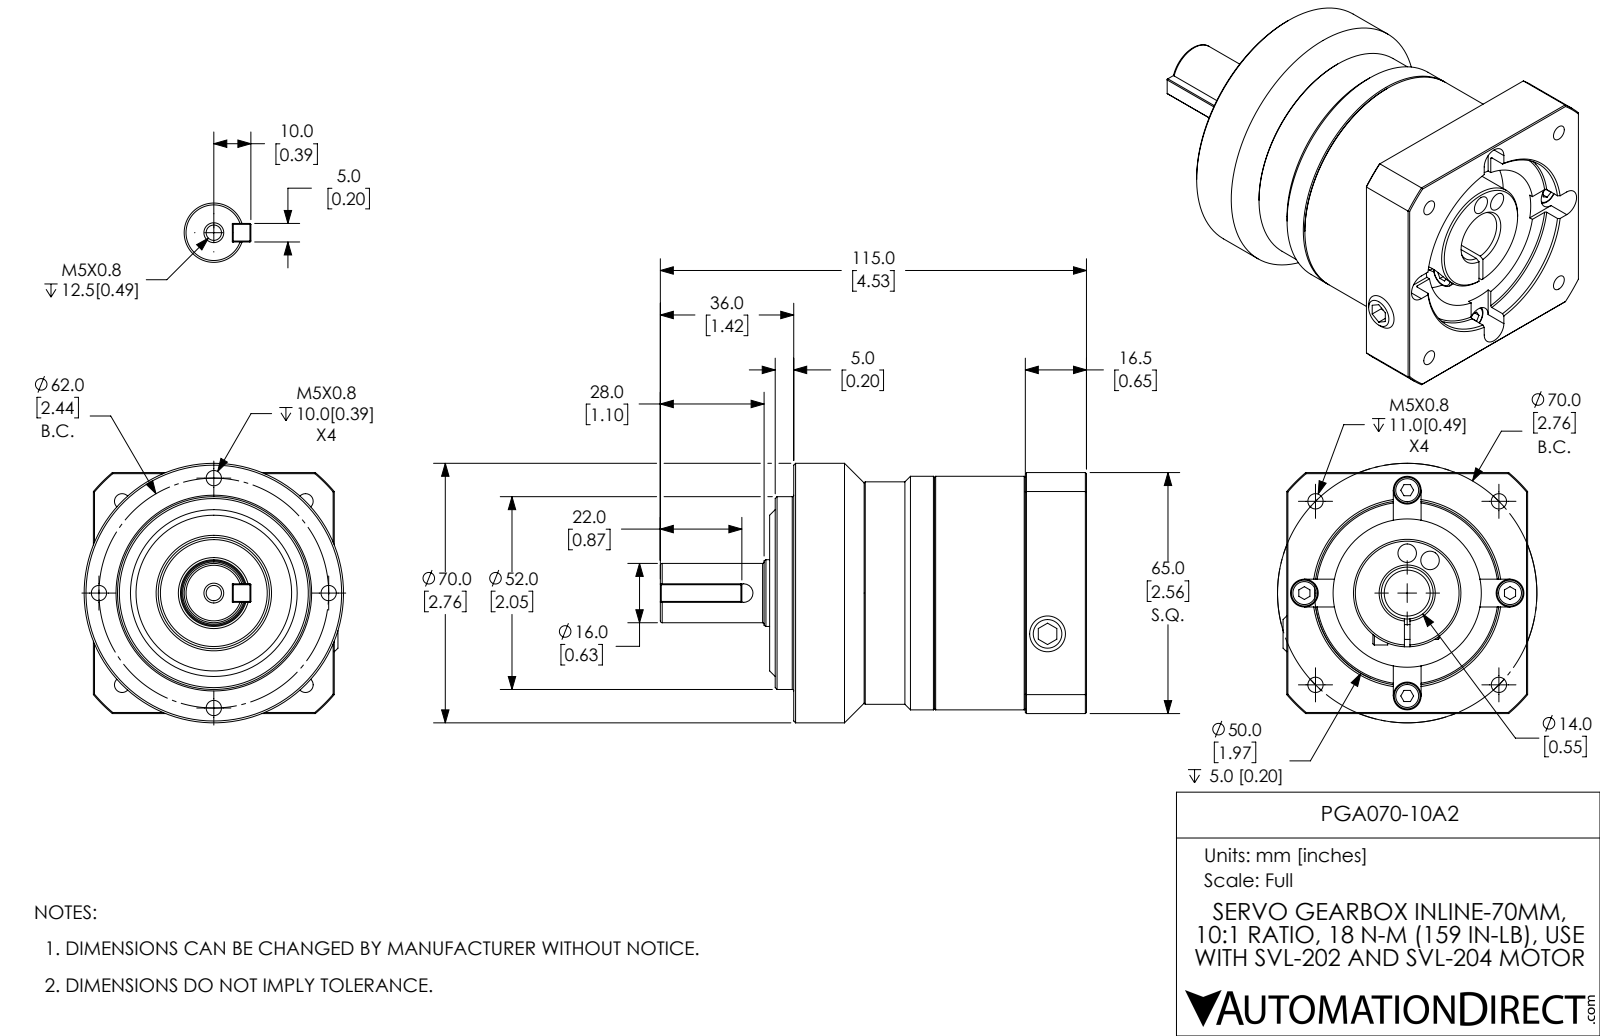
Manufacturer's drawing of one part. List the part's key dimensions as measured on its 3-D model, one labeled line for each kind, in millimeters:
Part name (STEP PRODUCT): PGA070-10A2
STEP written by: SolidWorks 2019 (CONFIG_CONTROL_DESIGN)
Units: millimetres
Bodies: 1 solid, 310 faces (127 planar, 81 cylindrical, 102 other)
Overall size (bounding box): 115 × 70 × 70
Volume: 263 976 mm³ · Surface area: 37 864 mm²
Round holes (diameter × count): ⌀4.13 ×9, ⌀7.5 ×4, ⌀5 ×2, ⌀4.5 ×1, ⌀8 ×1, ⌀14 ×1, ⌀29 ×1, ⌀40 ×1, ⌀50 ×1
Round bosses / shafts (diameter × count): ⌀7 ×5, ⌀70 ×1, ⌀63 ×1, ⌀60 ×1, ⌀52 ×1, ⌀18 ×1, ⌀16 ×1, ⌀4 ×1
Partial cylindrical surfaces — rounded edges, fillets, slot ends (radius × count): R1.62 ×1, R2.5 ×1, R4 ×1, R42.5 ×1
Main face-to-face distances: 79, 65, 16.5, 62.5, 5, 11.5, 6.5, 85.5, 69, 1.5
Hole centre spacings: 24.93, 25.53, 41.61, 58.04, 61, 3.25, 27.75, 31
